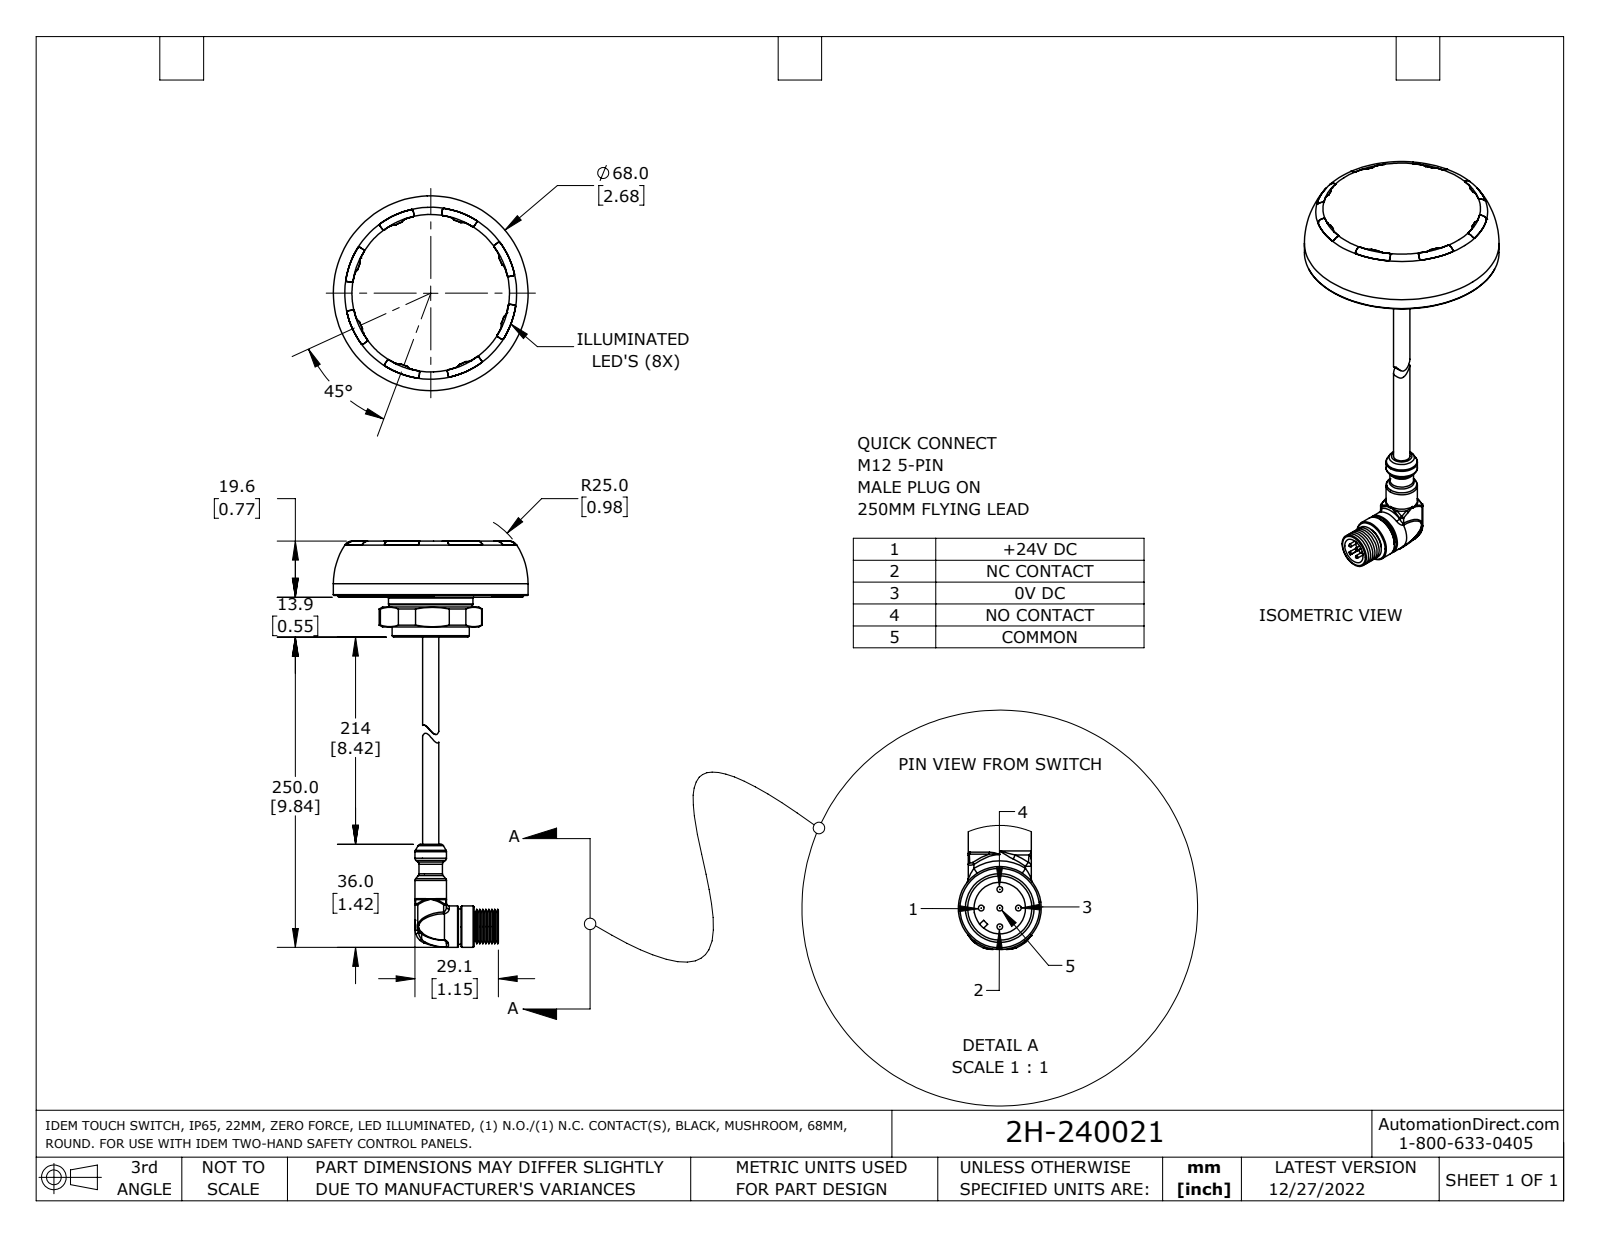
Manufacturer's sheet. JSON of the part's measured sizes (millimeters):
{"part_name": "2H-240021", "step_written_by": "SolidWorks 2021 (AUTOMOTIVE_DESIGN)", "units": "millimeters", "bodies": {"solids": 12, "faces": 1271, "planar": 237, "cylindrical": 482, "other": 552}, "overall_size": [141.8, 68, 68], "volume_mm3": 38800, "surface_area_mm2": 32860, "round_holes": [[2.1, 2], [3, 2], [3.3, 2], [8.8, 2], [9, 1], [22, 1], [25.4, 1], [30.5, 1], [58.4, 1], [64.8, 1]], "round_bosses_or_shafts": [[1, 5], [9.8, 2], [6.2, 2], [68, 1], [64.6, 1], [61.2, 1], [29.5, 1], [27, 1]], "partial_cylinders_radius": [[0.3, 121], [0.5, 87], [3, 16], [1, 4], [5, 3], [0.8, 2], [2.2, 2], [1, 1]], "face_to_face_distances": [1.4, 18.2, 19.6, 13.7, 4.5, 15.1, 15.9, 2.2, 2.3, 10.4], "hole_center_spacings": [24, 26.5, 35.7, 35.8, 48, 53]}
